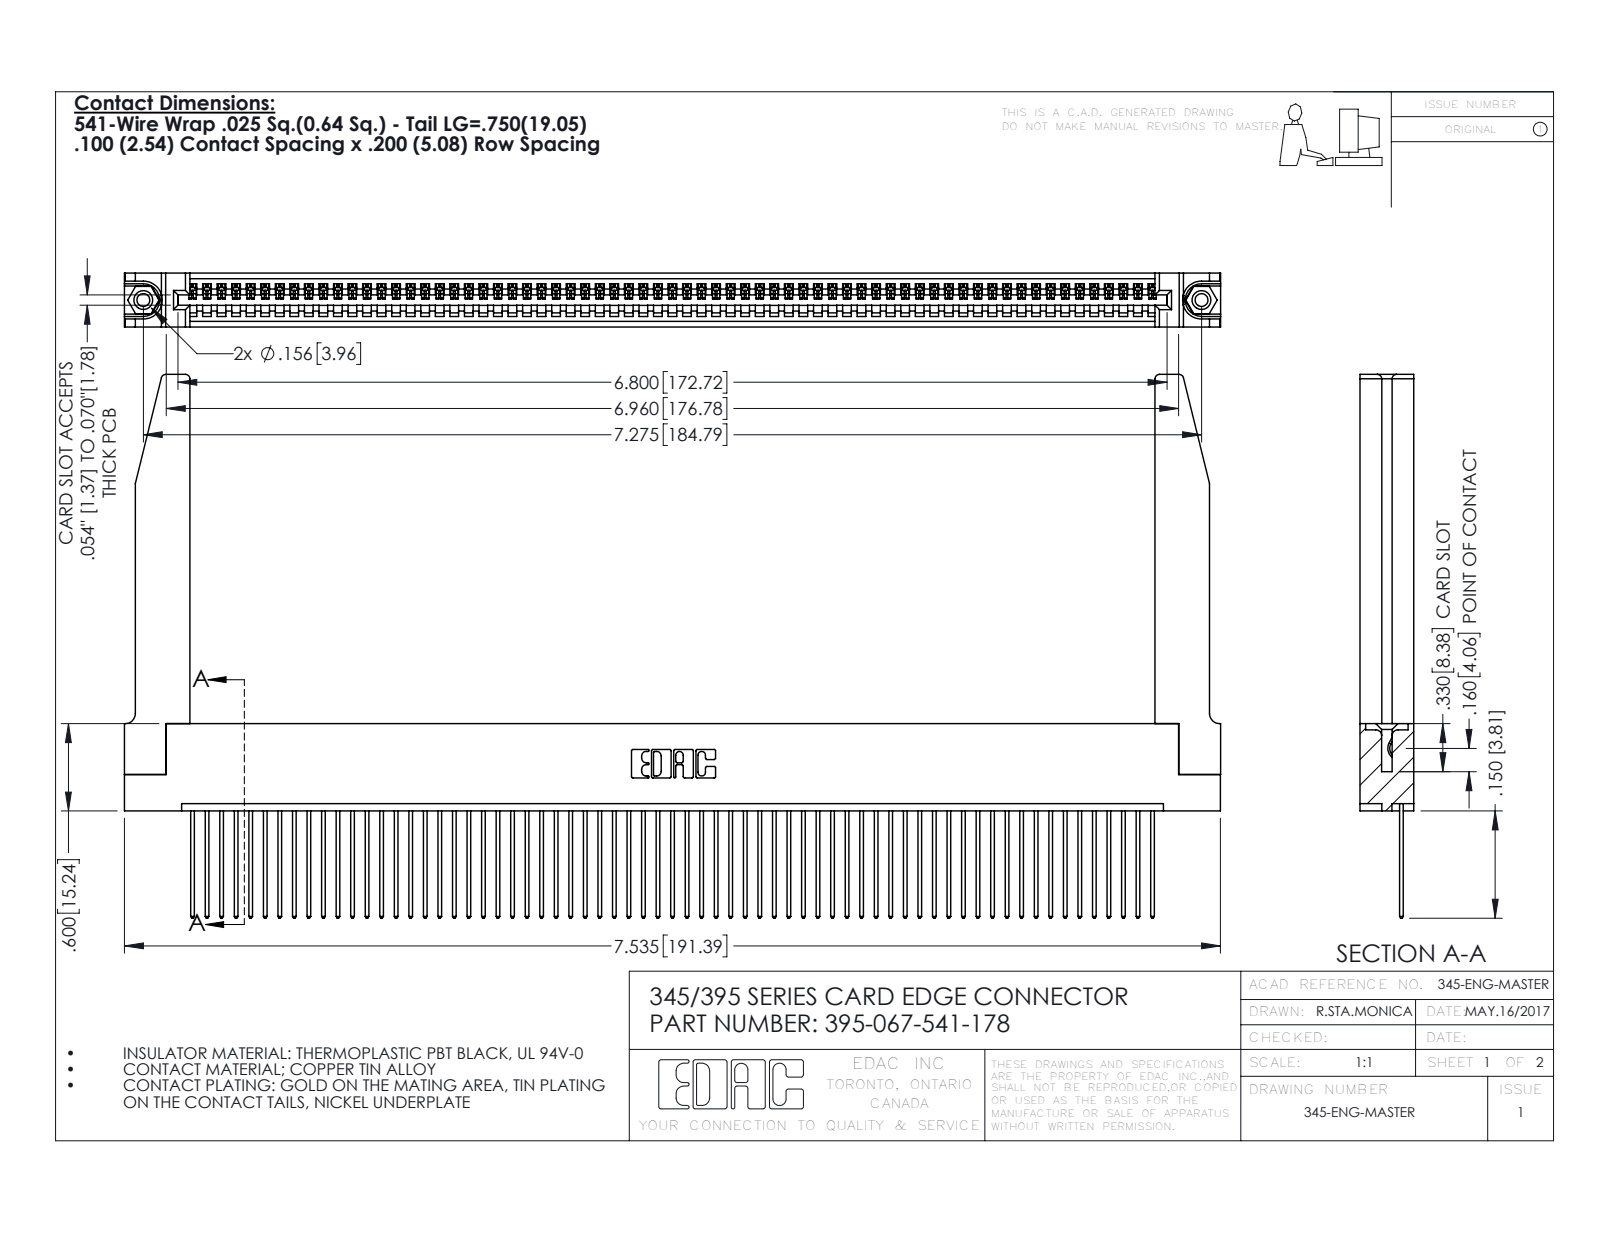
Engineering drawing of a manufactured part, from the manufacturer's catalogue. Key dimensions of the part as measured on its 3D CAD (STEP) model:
Part name (STEP PRODUCT): 345 Part_Flush Mounting Lugs - 0.156 Dia-TH; 395-067-541-178; 345-292-001_345-293-141; 345-220-078_345-220-078 (+1 more)
STEP written by: SolidWorks 2016 (CONFIG_CONTROL_DESIGN)
Units: inches
Bodies: 72 solids, 4246 faces (2902 planar, 1292 cylindrical, 52 other)
Overall size (bounding box): 7.536 × 3.737 × 0.37
Volume: 1.61 in³ · Surface area: 51.48 in²
Round holes (diameter × count): ⌀0.089 ×2, ⌀0.125 ×2, ⌀0.156 ×2, ⌀0.064 ×1
Round bosses / shafts (diameter × count): ⌀0.155 ×2
Partial cylindrical surfaces — rounded edges, fillets, slot ends (radius × count): R0.006 ×134, R0.01 ×134, R0.01 ×22, R0.03 ×8, R0.007 ×6, R0.031 ×6, R0.026 ×3, R0.031 ×2
Main face-to-face distances: 0.072, 0.298, 0.37, 0.098, 0.272, 0.025, 0.2, 0.225, 0.149, 0.148
Hole centre spacings: 0.27, 7.039, 7.275
